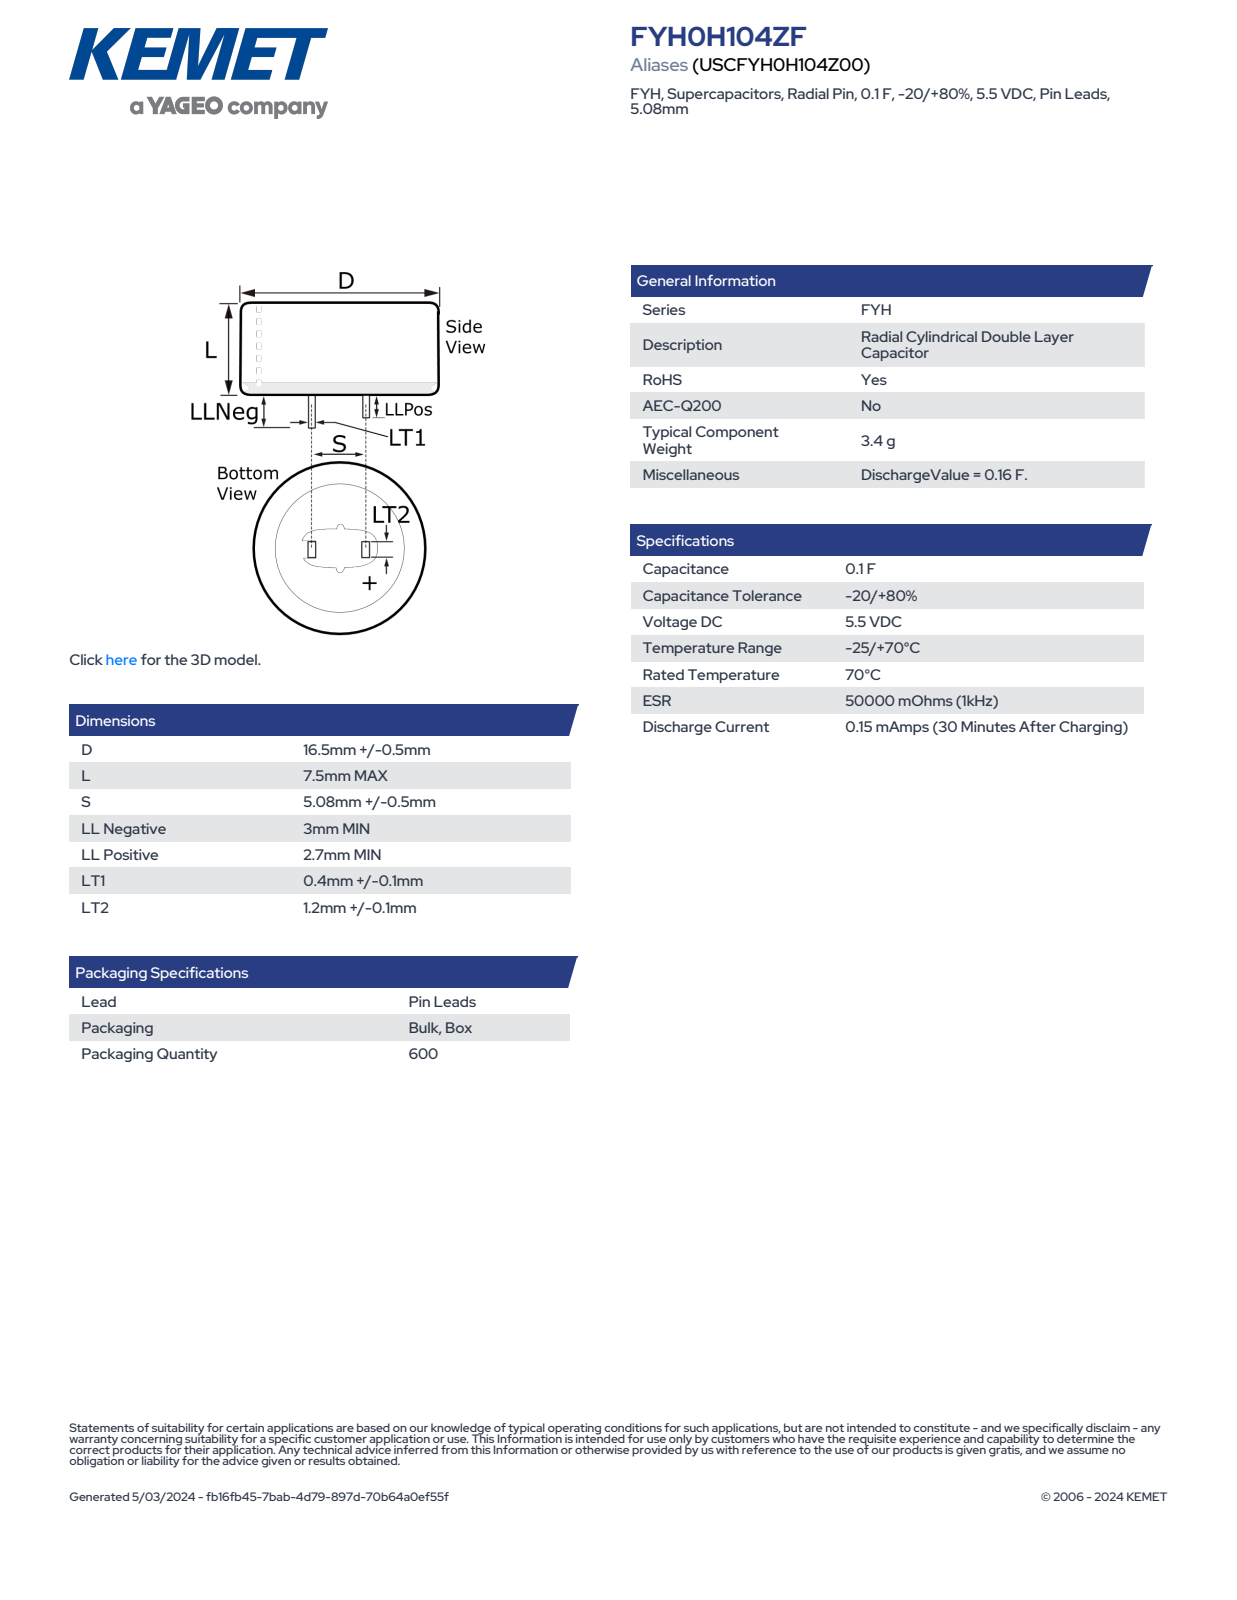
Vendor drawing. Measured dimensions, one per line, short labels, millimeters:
name: CDR_LPLLN_D17L7.5S5.08LLNEG3LLPOS2.7LT10.5LT21.3
written by: SolidWorks 2014 (AUTOMOTIVE_DESIGN)
unit: mm
bodies: 1 solid, 78 faces (70 planar, 4 cylindrical, 4 other)
size: 17 × 17 × 10.5
volume: 1 701 mm³; area: 853 mm²
bosses: 1× ⌀17
rounds: 1× R8.51
face distances: 7.5, 0.5, 5.08, 5.58, 4.58, 1.3, 3, 10.5, 2.7, 10.2
